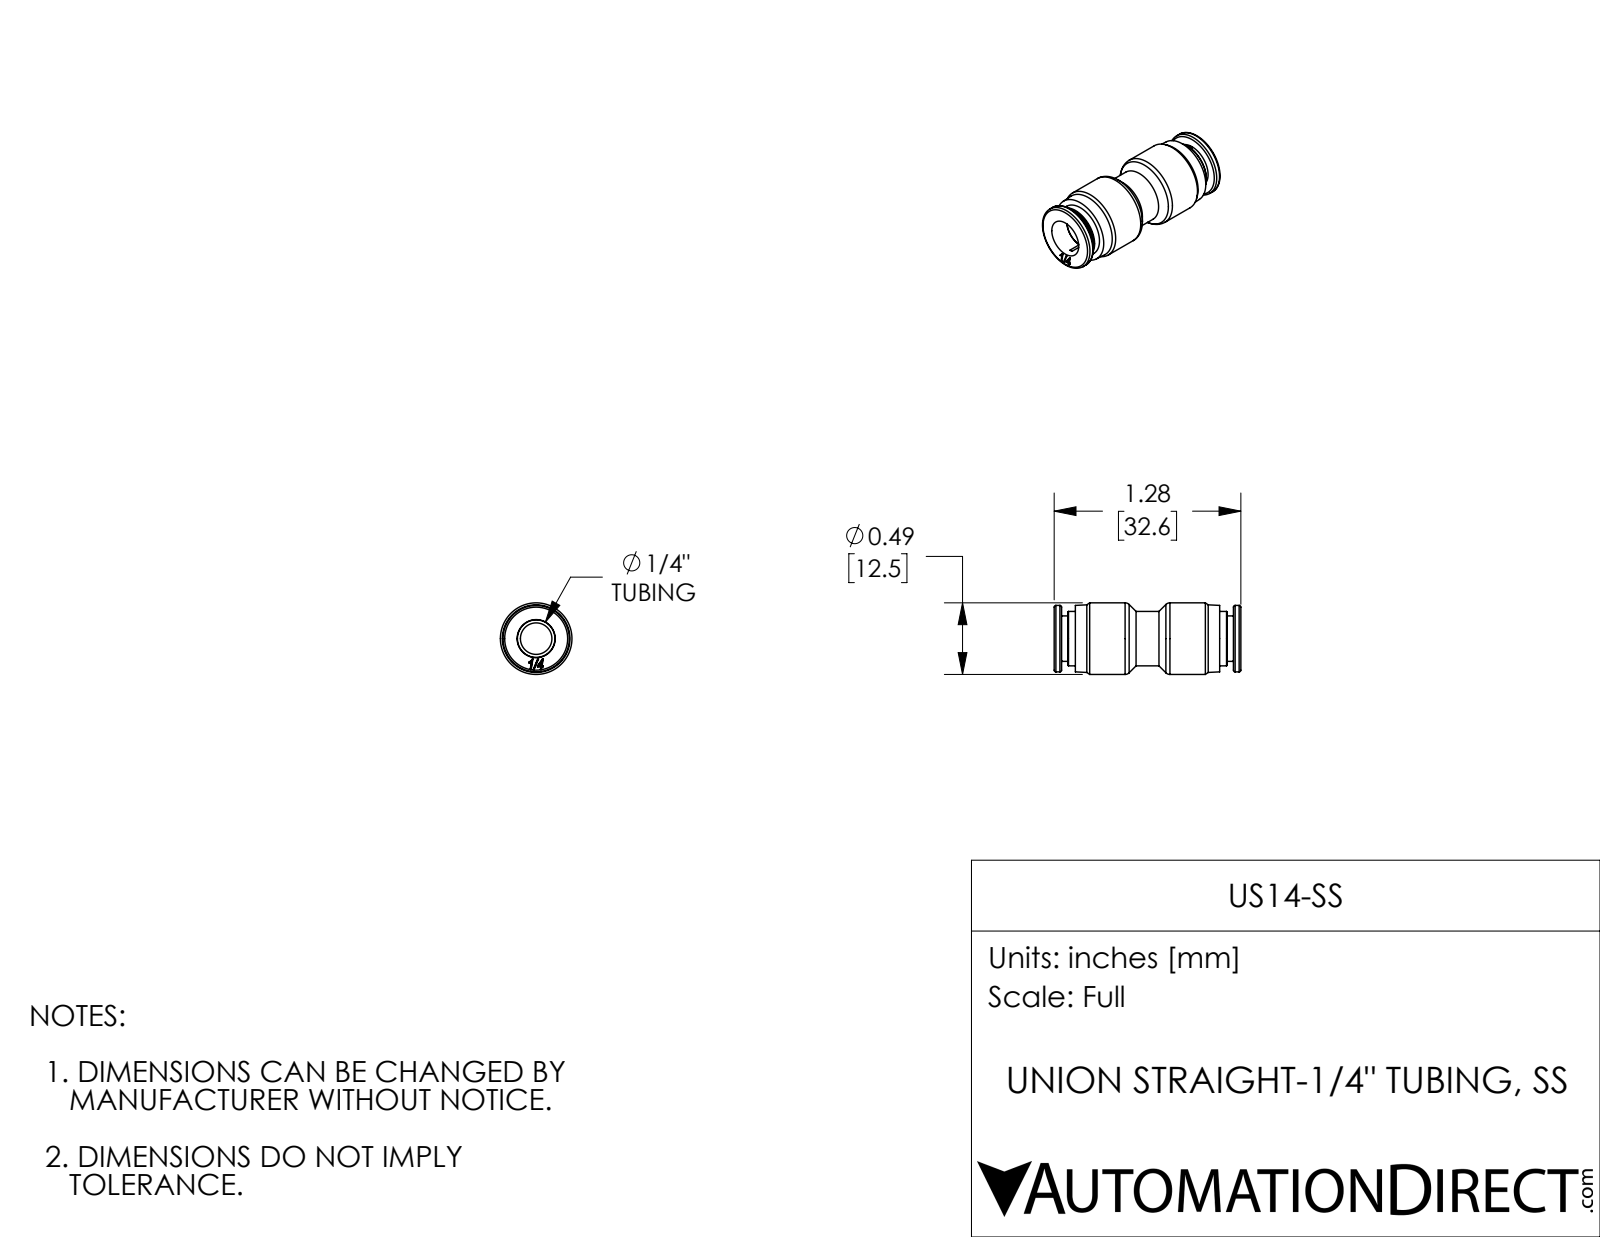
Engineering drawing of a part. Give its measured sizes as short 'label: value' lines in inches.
name: US14-SS
written by: SolidWorks 2017 (AUTOMOTIVE_DESIGN)
unit: in
bodies: 1 solid, 150 faces (78 planar, 32 cylindrical, 40 other)
size: 1.283 × 0.492 × 0.492
volume: 0.133 in³; area: 3.669 in²
holes: 1× ⌀0.217, 1× ⌀0.258, 1× ⌀0.262, 1× ⌀0.319
bosses: 1× ⌀0.492, 1× ⌀0.457, 1× ⌀0.374, 1× ⌀0.313
face distances: 0.051, 0.094, 1.138, 1.232, 0.146, 1.087, 1.283, 1.181, 0.992, 0.622
